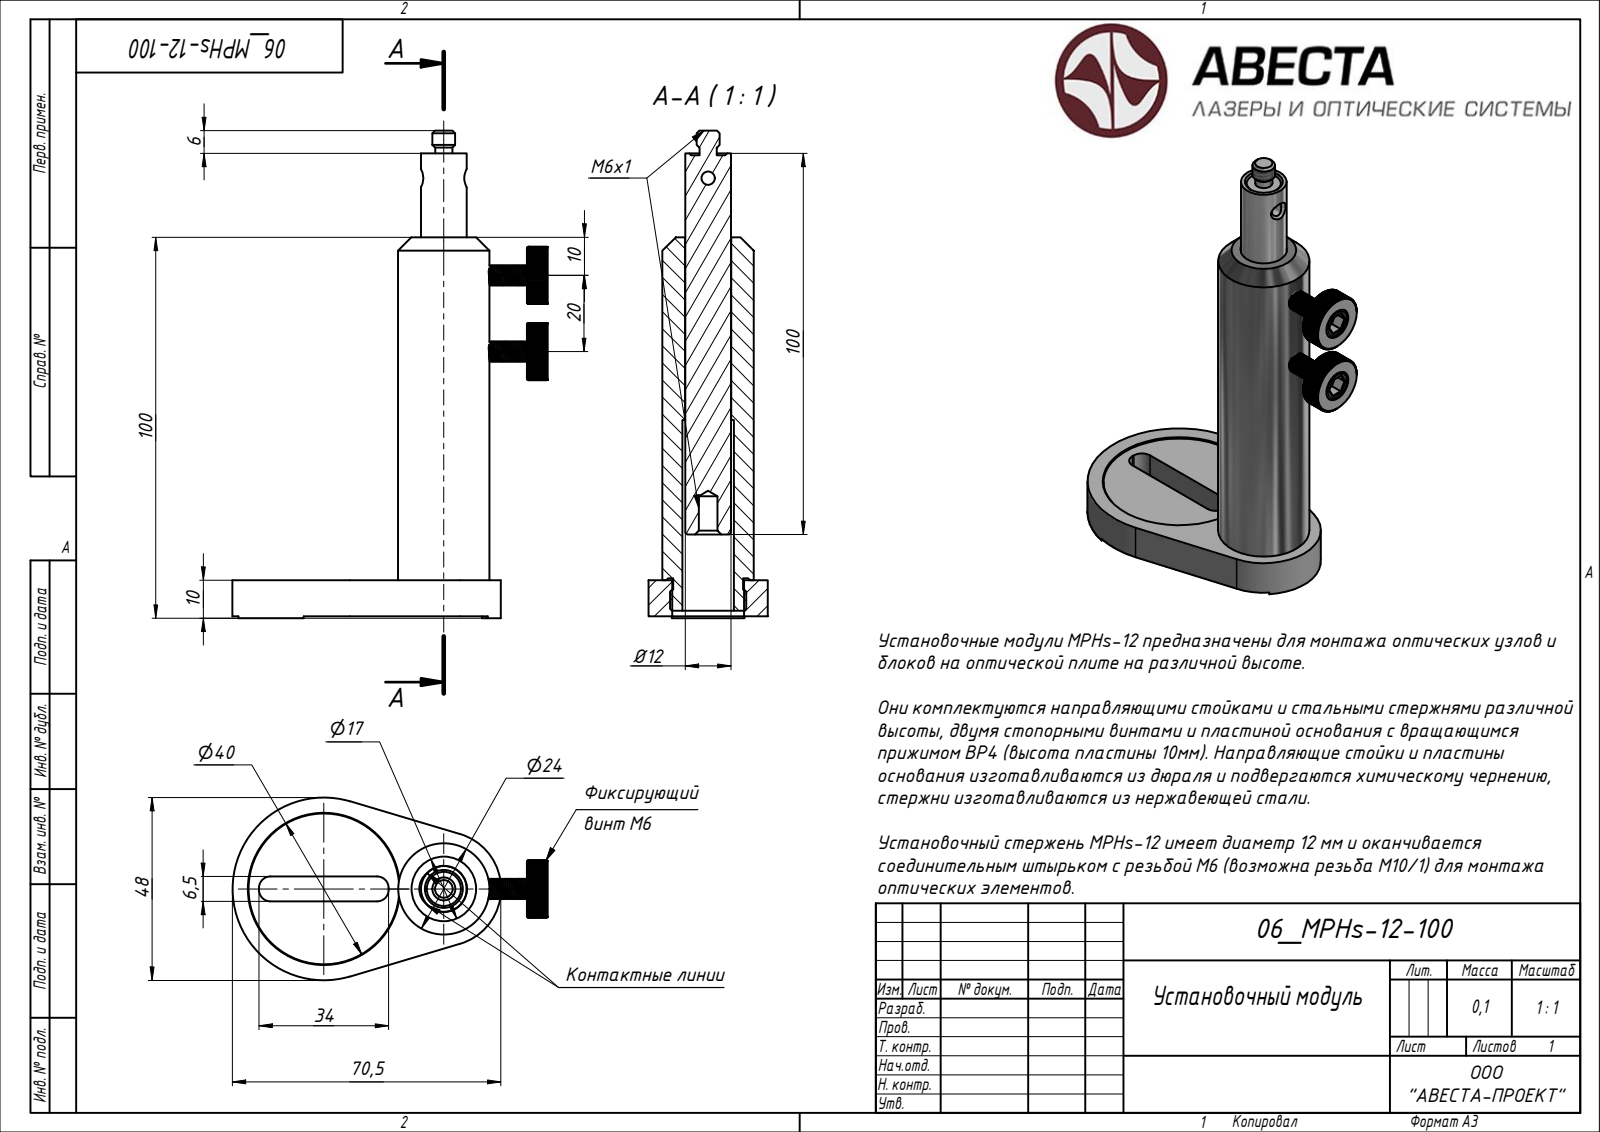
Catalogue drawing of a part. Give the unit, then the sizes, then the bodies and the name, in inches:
Units: inches
Overall size (bounding box): 11.887 × 10.322 × 6.22
Main face-to-face distances: 0.059, 0.374, 0.315, 0.362, 0.303, 0.059, 0.315, 0.303, 0.059, 0.374
Volume: 36.73 in³ · Surface area: 456.4 in²
Bodies: 105 solids, 8449 faces (4704 planar, 0 cylindrical, 3745 other)
STEP written by: ST-DEVELOPER v15 (AUTOMOTIVE_DESIGN)
